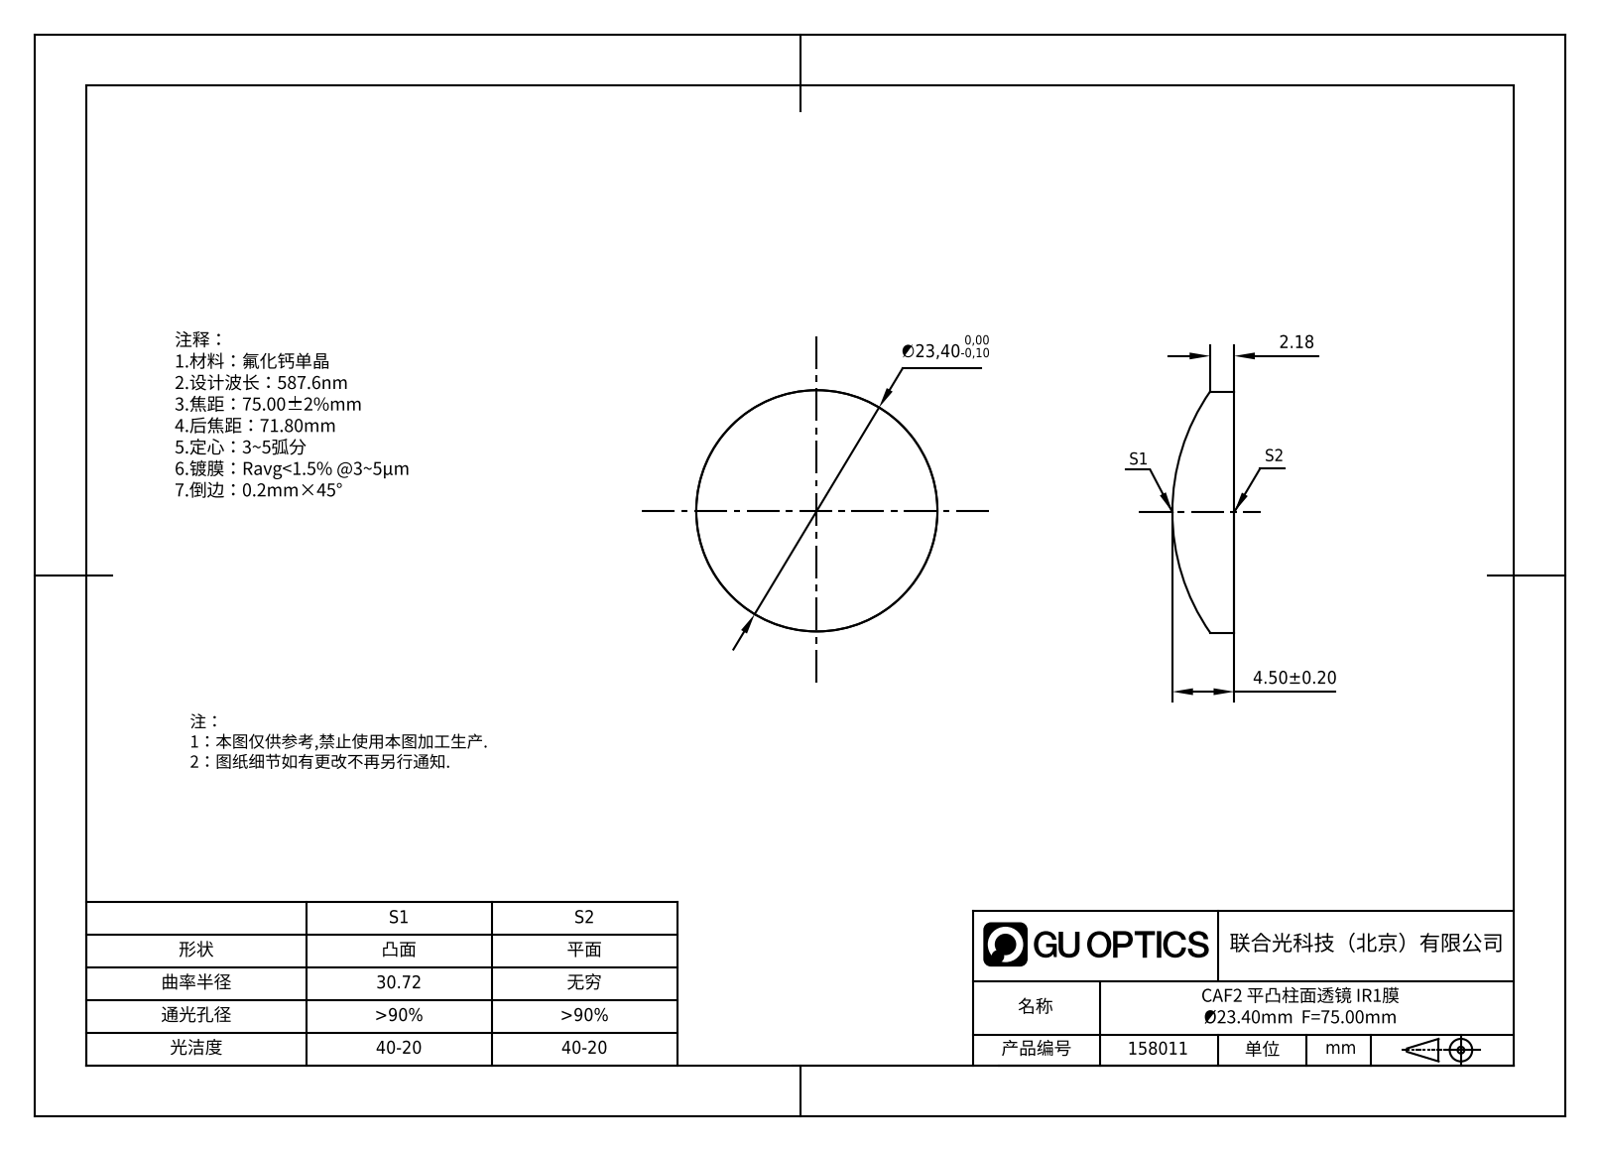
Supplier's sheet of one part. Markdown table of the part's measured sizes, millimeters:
| quantity | value |
| --- | --- |
| part name | GL55-025-075-IR1 |
| STEP written by | SolidWorks 2022 (AUTOMOTIVE_DESIGN) |
| units | millimeters |
| bodies | 1 solid, 9 faces (1 planar, 4 cylindrical, 4 other) |
| overall size | 23.4 × 23.4 × 4.5 |
| volume | 1 682 mm³ |
| surface area | 1 099 mm² |
| round bosses / shafts (diameter × count) | 23.4 × 1 |
| partial cylindrical surfaces (radius × count) | 30.72 × 1 |
